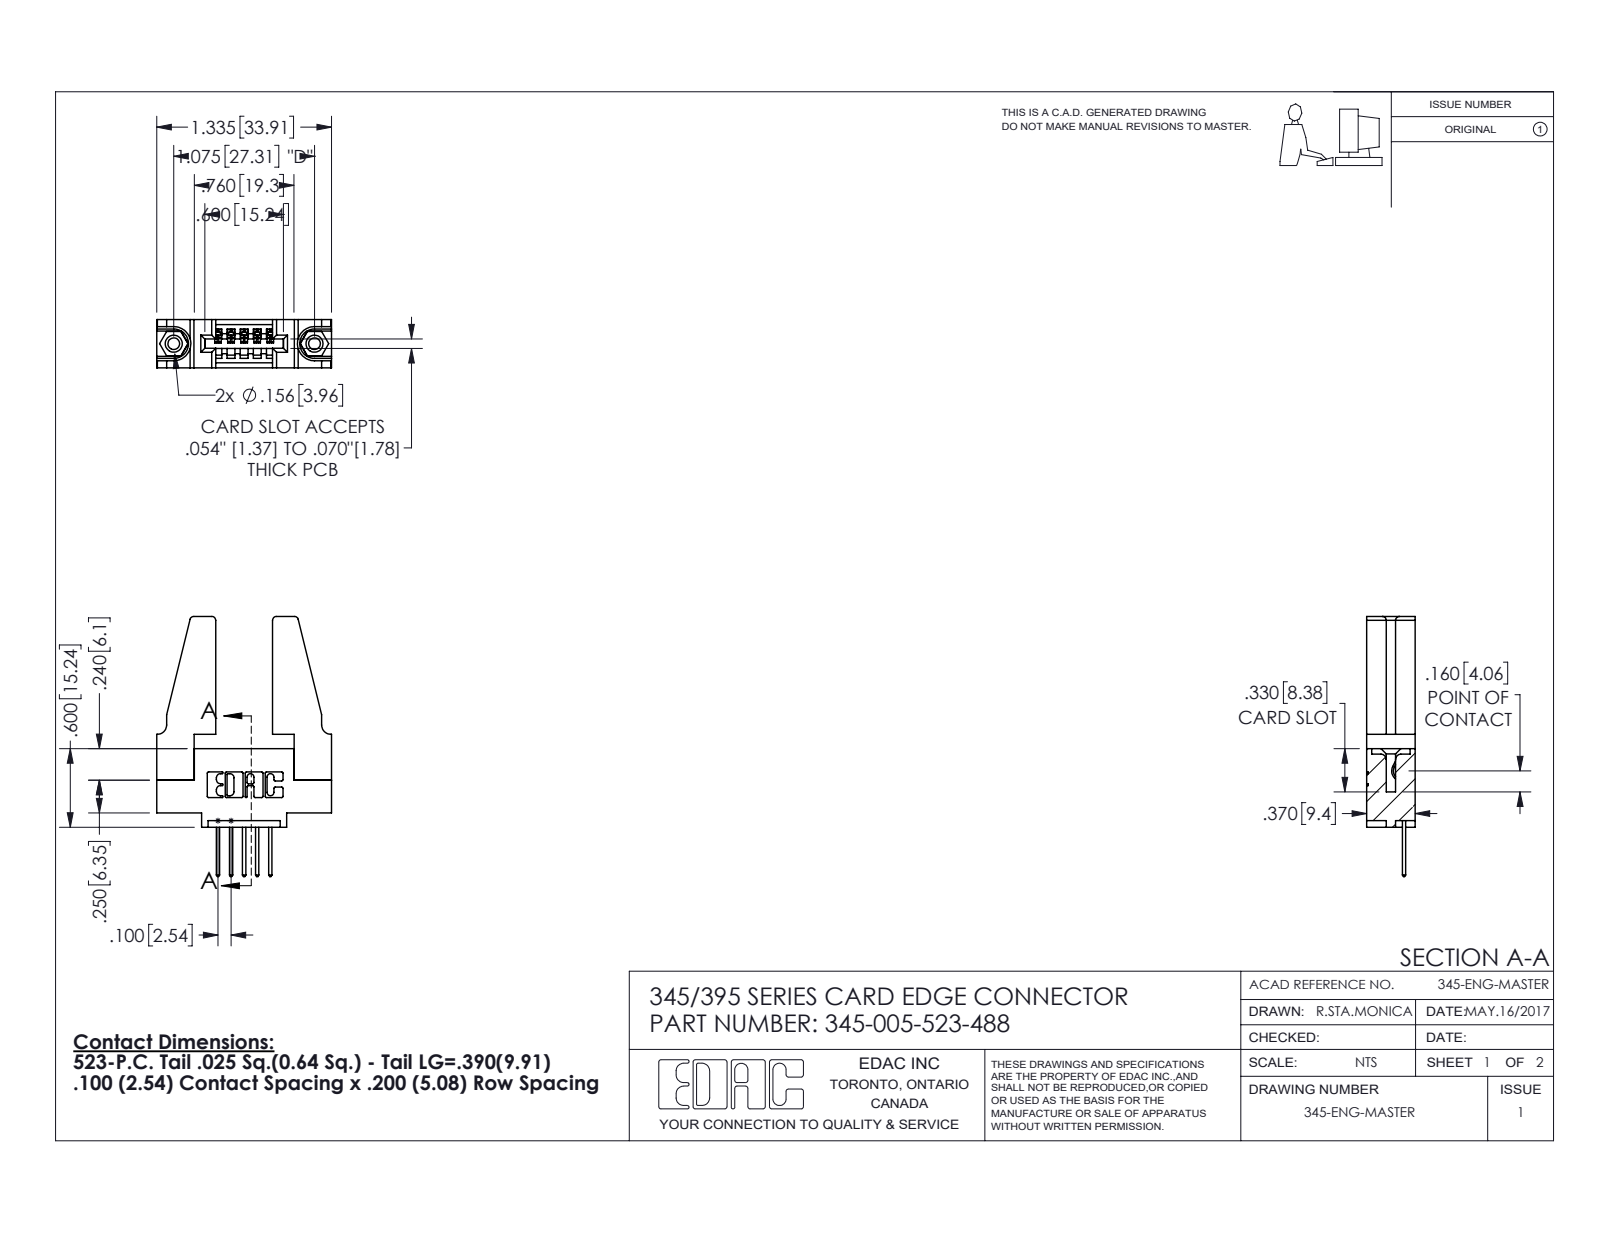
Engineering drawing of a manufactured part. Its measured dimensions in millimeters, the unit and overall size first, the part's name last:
Units: millimetres
Overall size (bounding box): 50.5 × 33.9 × 9.4
Round holes (diameter × count): ⌀2.3 ×2, ⌀3.2 ×2, ⌀4 ×2, ⌀1.6 ×1
Round bosses / shafts (diameter × count): ⌀3.9 ×2
Partial cylindrical surfaces — rounded edges, fillets, slot ends (radius × count): R0.3 ×22, R0.2 ×10, R0.3 ×10, R0.8 ×8, R0.2 ×6, R0.8 ×6, R0.7 ×3, R0.8 ×2
Main face-to-face distances: 9.4, 1.8, 7.6, 5.1, 3.8, 3.8, 5.6, 2, 11.4, 7.3
Hole centre spacings: 6.9, 21.5, 27.3
Volume: 6 100 mm³ · Surface area: 6 497 mm²
Bodies: 10 solids, 544 faces (356 planar, 172 cylindrical, 16 other)
Part name (STEP PRODUCT): 345-005-523-488; 345-250-001_345-250-001-102; 345-220-078_345-220-088; 345-292-001_345-293-123 (+1 more)
STEP written by: SolidWorks 2016 (CONFIG_CONTROL_DESIGN)
